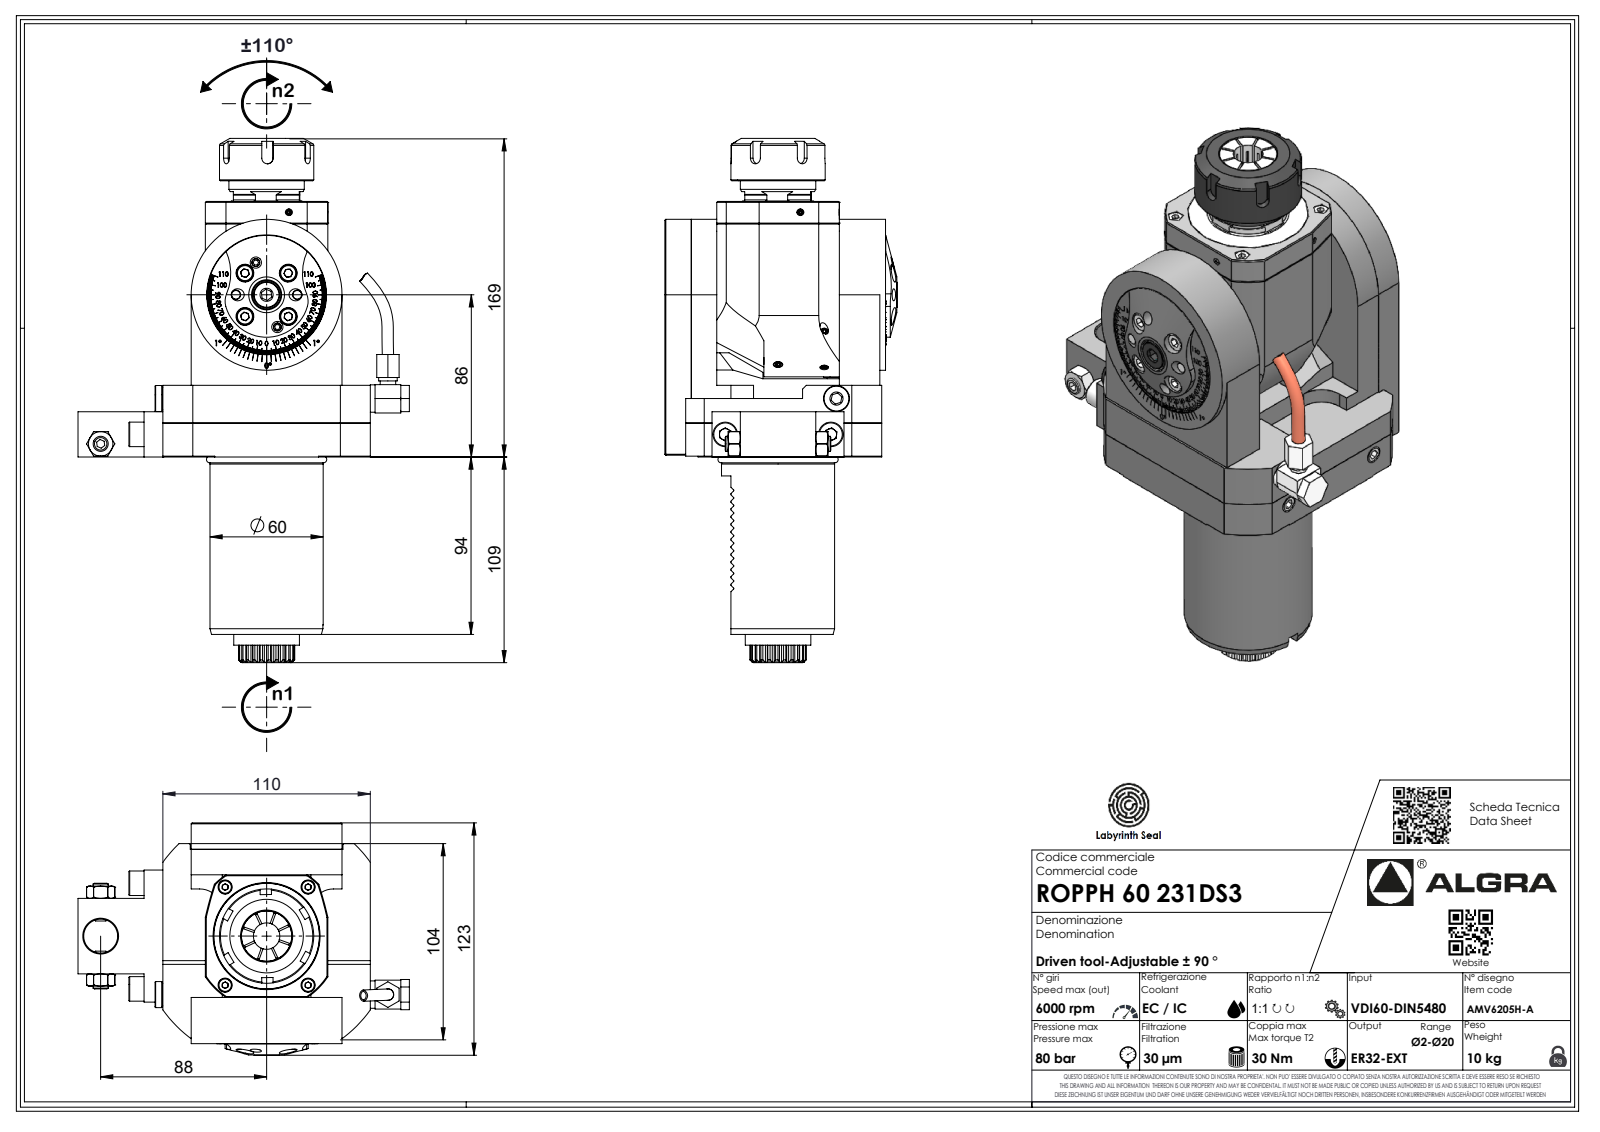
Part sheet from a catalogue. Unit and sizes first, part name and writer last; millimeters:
Units: millimetres
Overall size (bounding box): 277.91 × 175.7 × 123
Round holes (diameter × count): ⌀2.1 ×1, ⌀50 ×1
Round bosses / shafts (diameter × count): ⌀80 ×1, ⌀60 ×1, ⌀58.7 ×1, ⌀40 ×1, ⌀34.8 ×1, ⌀14.5 ×1, ⌀9.8 ×1, ⌀8.2 ×1
Partial cylindrical surfaces — rounded edges, fillets, slot ends (radius × count): R0.3 ×14, R0.33 ×7, R0.52 ×7, R3.7 ×7, R3 ×5, R0.2 ×3, R10 ×2, R12 ×2
Main face-to-face distances: 22.5, 87.5, 65, 80, 7.5, 95, 15, 7, 135.5, 27.5
Volume: 1 236 000 mm³ · Surface area: 124 080 mm²
Bodies: 1 solid, 924 faces (594 planar, 166 cylindrical, 164 other)
Part name (STEP PRODUCT): ROPPH60231DS3
STEP written by: SolidWorks 2023 (AUTOMOTIVE_DESIGN)
